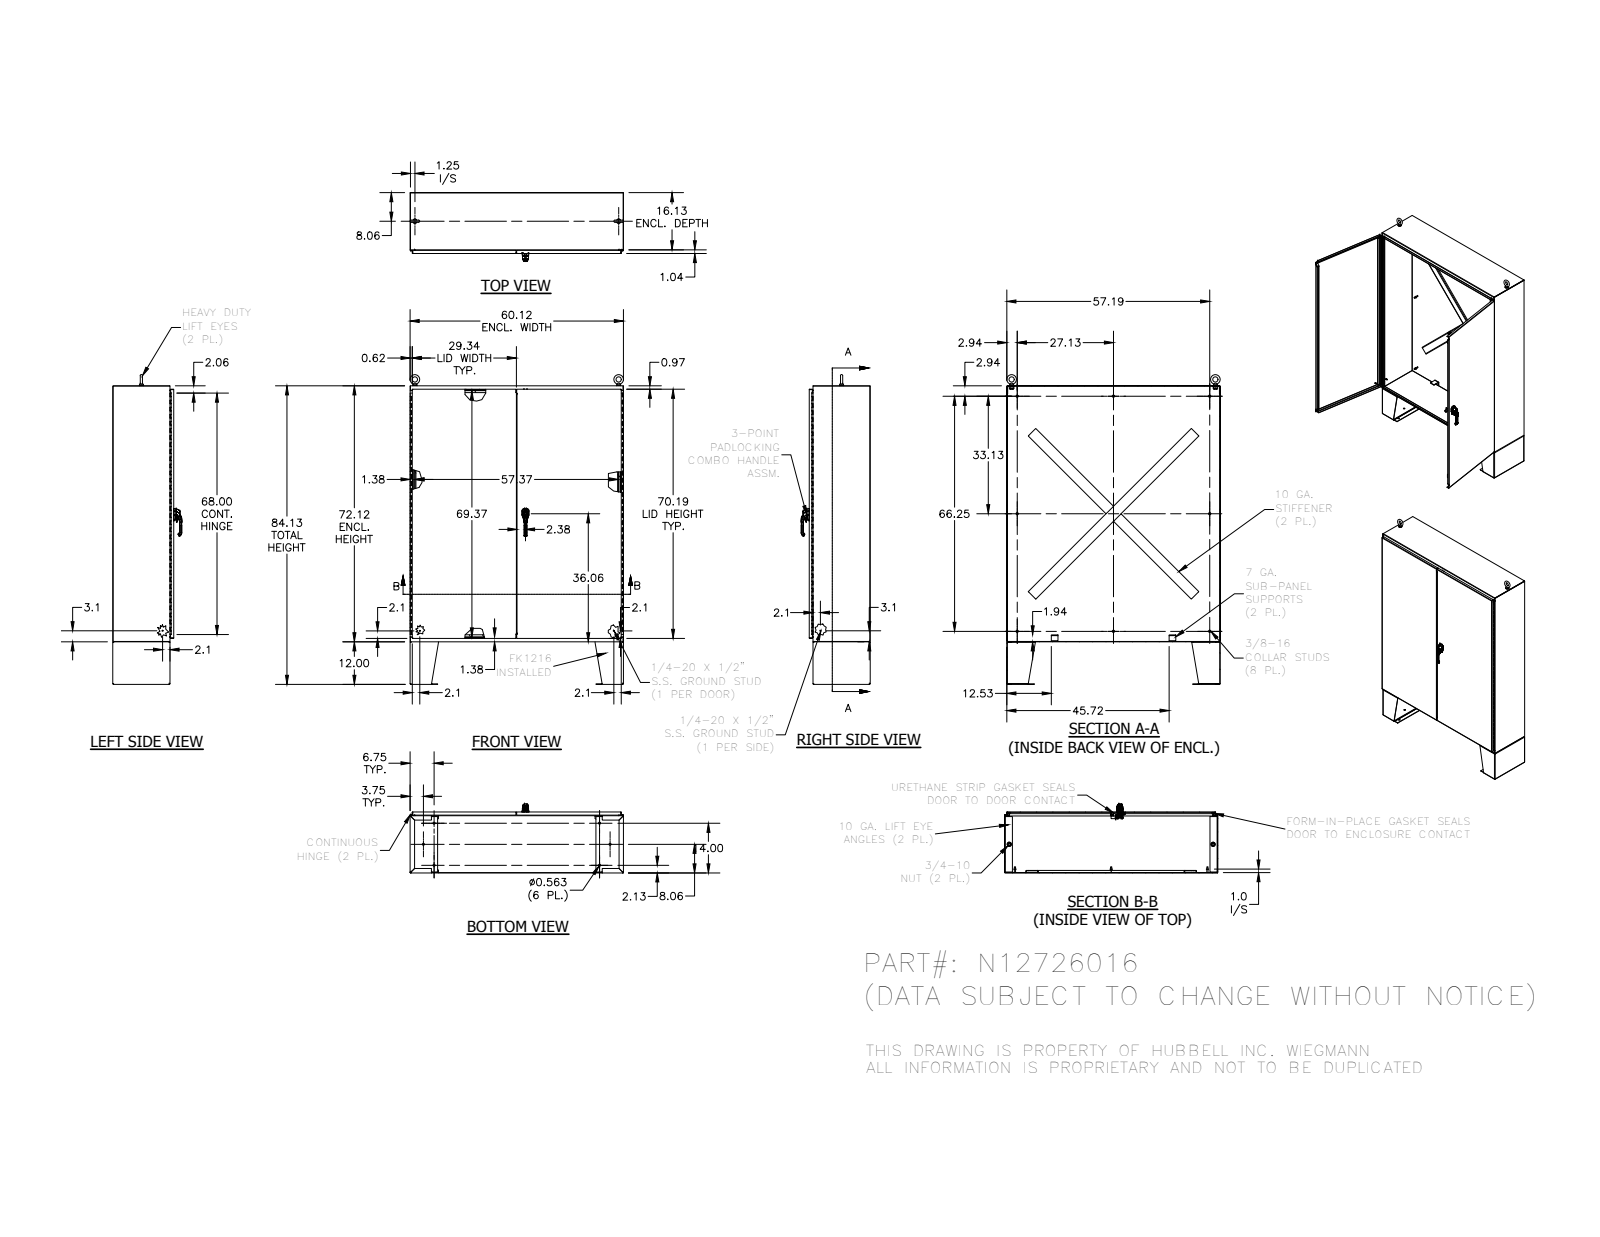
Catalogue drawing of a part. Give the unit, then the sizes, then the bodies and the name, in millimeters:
Units: millimetres
Overall size (bounding box): 2216.1 × 1527.2 × 491.2
Round holes (diameter × count): ⌀14.3 ×18, ⌀7 ×8, ⌀5.1 ×4, ⌀7.1 ×3, ⌀3.2 ×2, ⌀3.2 ×2, ⌀6.1 ×2, ⌀6.4 ×2, ⌀6.4 ×2, ⌀10.2 ×2, ⌀11.4 ×2, ⌀16.3 ×2
Round bosses / shafts (diameter × count): ⌀8.4 ×8, ⌀15.9 ×5, ⌀6.4 ×5, ⌀15.9 ×3, ⌀8.6 ×3, ⌀31.8 ×2, ⌀28.4 ×2, ⌀25.4 ×2
Partial cylindrical surfaces — rounded edges, fillets, slot ends (radius × count): R0.8 ×24, R2.4 ×23, R5.6 ×22, R1.3 ×18, R0.6 ×16, R3.2 ×15, R0.8 ×13, R1.7 ×8
Main face-to-face distances: 2.4, 433.5, 431.1, 435.9, 1524.8, 1829.6, 1527.2, 1522.4, 1827.2, 1832
Hole centre spacings: 127, 148.6, 166.9, 169, 204, 374.7, 395.6, 1178.5
Volume: 26 430 000 mm³ · Surface area: 21 020 000 mm²
Bodies: 76 solids, 2596 faces (1528 planar, 768 cylindrical, 300 other)
Part name (STEP PRODUCT): N12726016
STEP written by: SolidWorks 2018 (AUTOMOTIVE_DESIGN)
